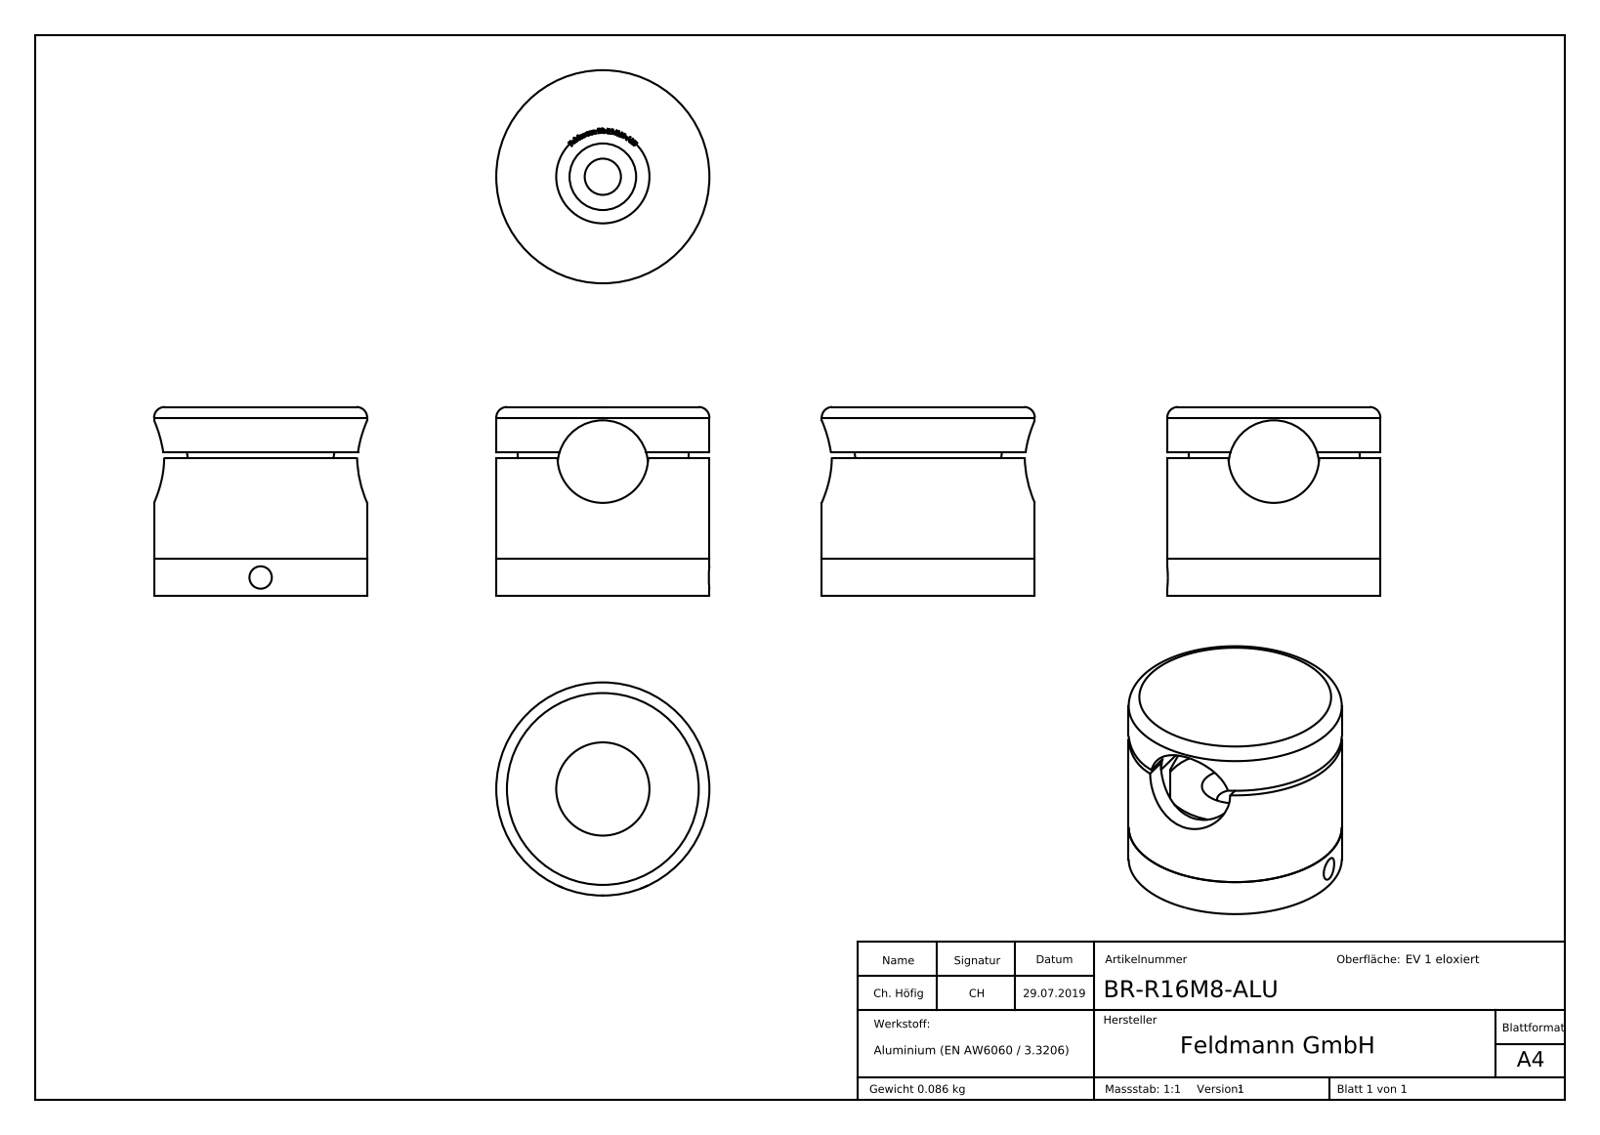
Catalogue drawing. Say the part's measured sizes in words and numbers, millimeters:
The part is named "BR-R1XM8-XXX Teil2; BR-R1XM8-XXX Teil1_BR-16M8-ALU Teil1; BR-R16M8-ALU; BR-R1XM8-XXX Teil3 (+3 more)". Its 3-D file was written by "SolidWorks 2015 (CONFIG_CONTROL_DESIGN)". It is 3 solids with 324 faces: 185 planar, 15 cylindrical and 124 other. Overall it measures 64.34 by 40 by 40 millimeters. Its volume is 31 710 cubic millimeters and its surface area 15 148 square millimeters. Round holes: 1 of diameter 4.2, 1 of diameter 6.8, 1 of diameter 12.5, 1 of diameter 32.5. Round bosses or shafts: 1 of diameter 40, 1 of diameter 28. Partial cylindrical surfaces (rounded edges, fillets, slot ends): 2 of radius 8.5, 1 of radius 13.25, 1 of radius 16.05. The main face-to-face distances are 7, 35.5, 28.5, 19.5, 16, 9, 8.5, 27, 20, 11.
